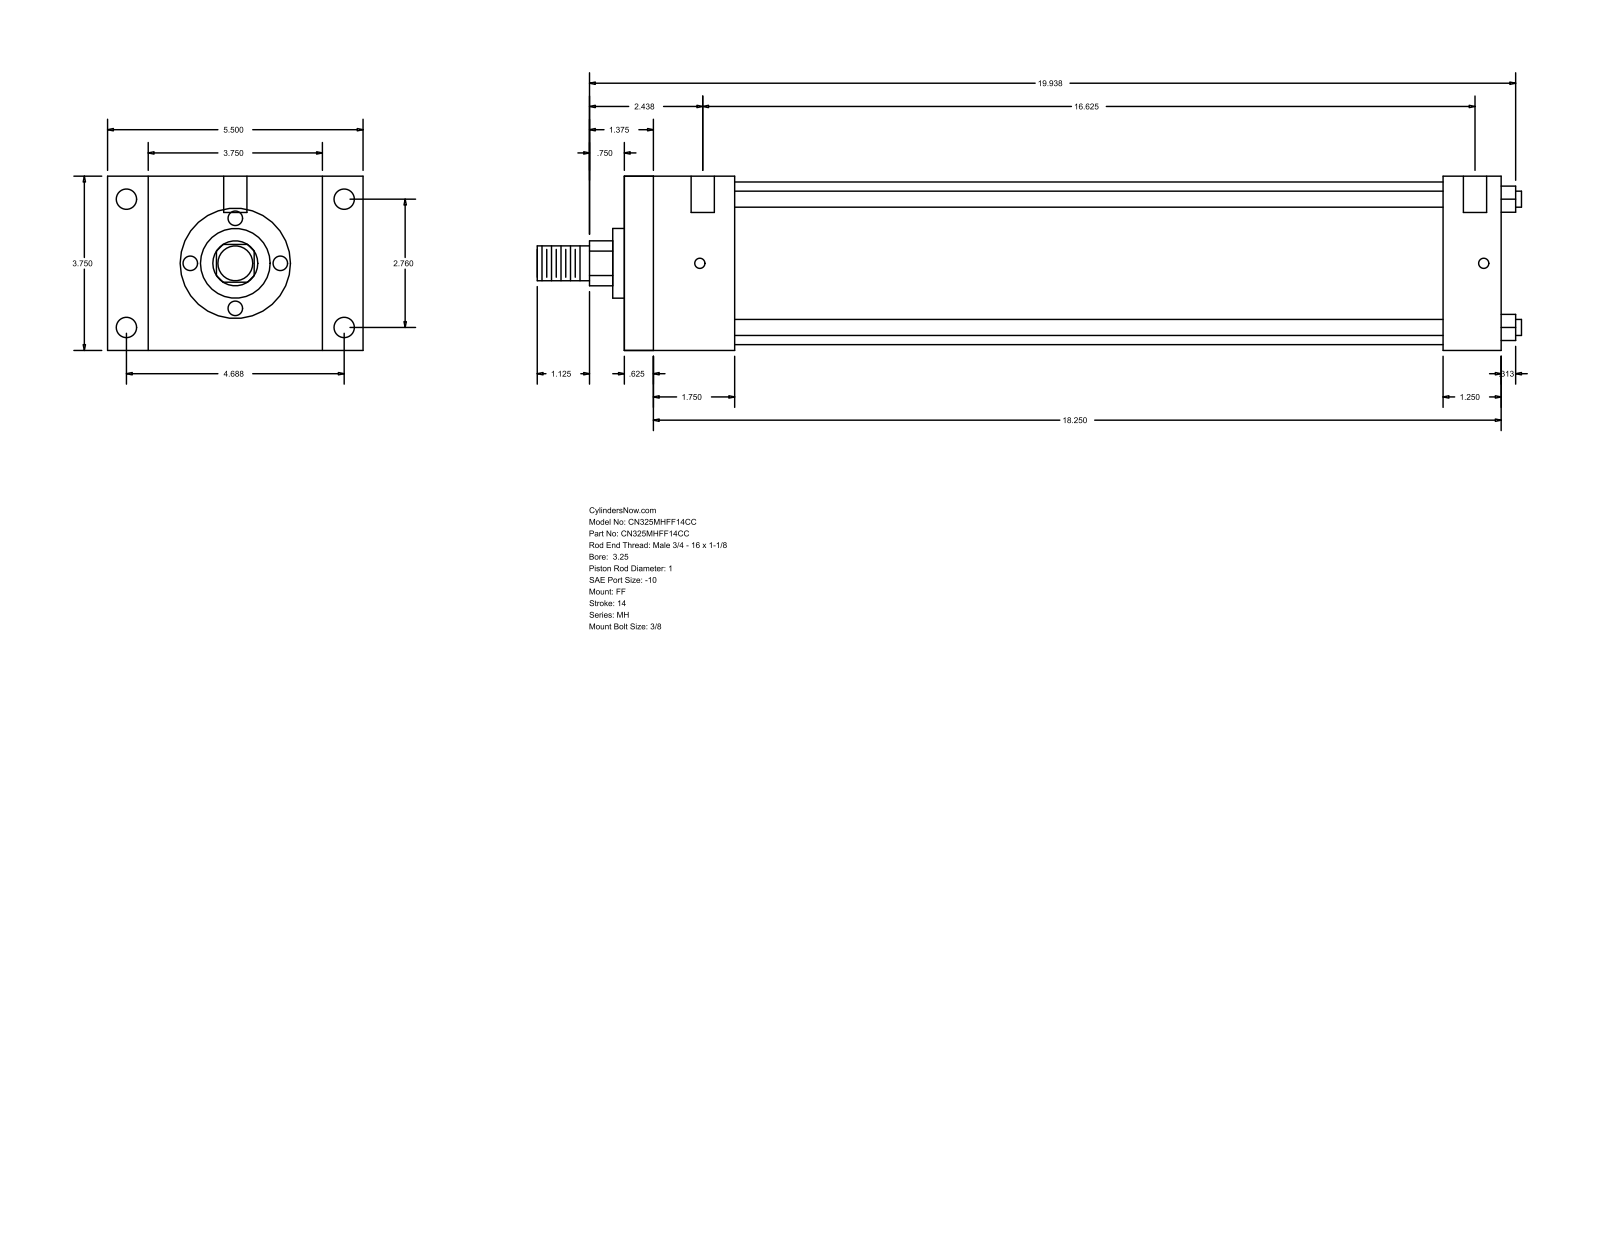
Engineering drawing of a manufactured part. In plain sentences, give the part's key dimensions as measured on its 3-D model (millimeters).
The part is named "MH_FF__0325_1". Its 3-D file was written by "GSSL Pune (CONFIG_CONTROL_DESIGN)". It is 0 solids with 92 faces: 64 planar, 28 cylindrical and 0 other. Overall it measures 538.16 by 139.7 by 95.25 millimeters. Round holes: 4 of diameter 5.56, 4 of diameter 11.13, 2 of diameter 12.7. Round bosses or shafts: 4 of diameter 8.76, 1 of diameter 88.9, 1 of diameter 38.1, 1 of diameter 25.4, 1 of diameter 19.05. Partial cylindrical surfaces (rounded edges, fillets, slot ends): 1 of radius 12.29. The main face-to-face distances are 95.24, 479.43, 15.87, 463.56, 22.23, 117.47, 447.68, 431.81, 31.75, 60.33. The hole center spacings are 70.1, 119.06, 138.16, 428.62, 1.58, 4.76, 422.28, 423.86.
